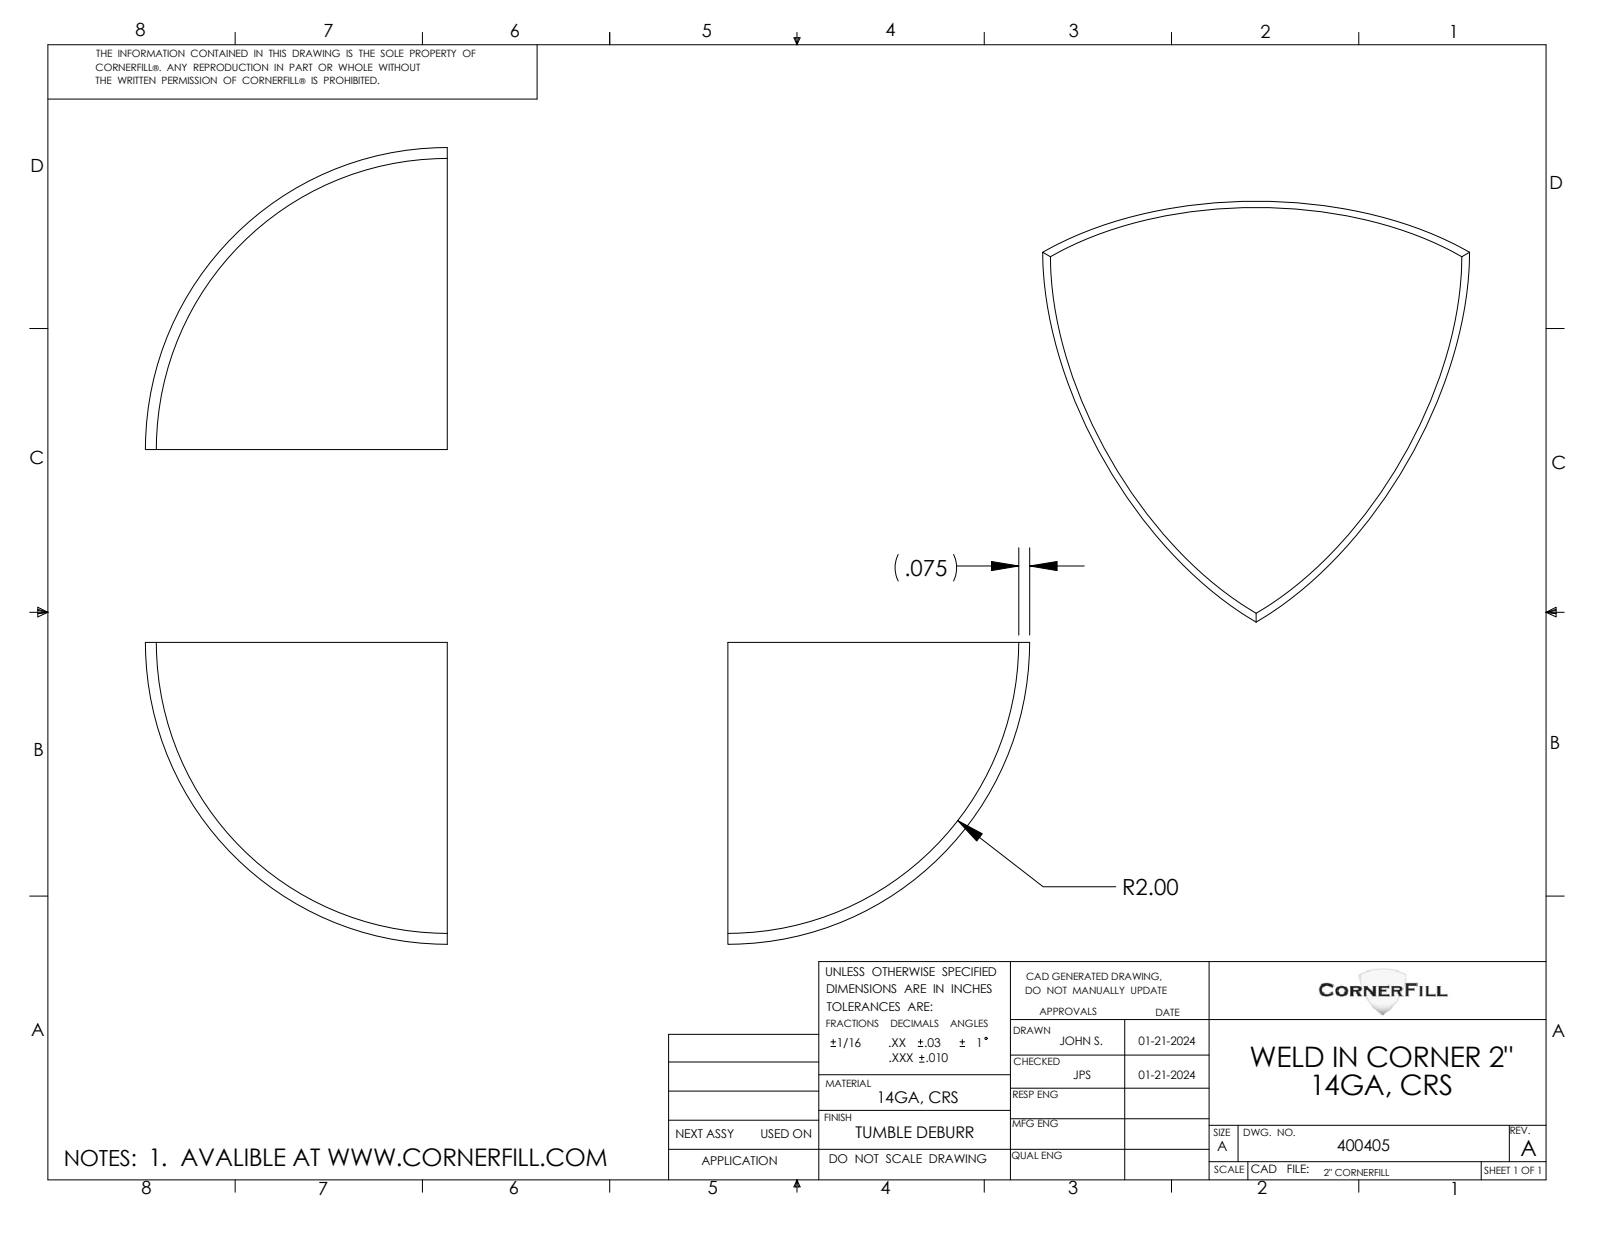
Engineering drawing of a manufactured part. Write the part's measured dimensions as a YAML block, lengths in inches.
part_name: "400405"
step_written_by: "SolidWorks 2021 (CONFIG_CONTROL_DESIGN)"
units: inches
bodies: {solids: 1, faces: 5, planar: 3, cylindrical: 0, other: 2}
overall_size: [2.934, 2.075, 2.075]
volume: 0.489
surface_area: 13.77
